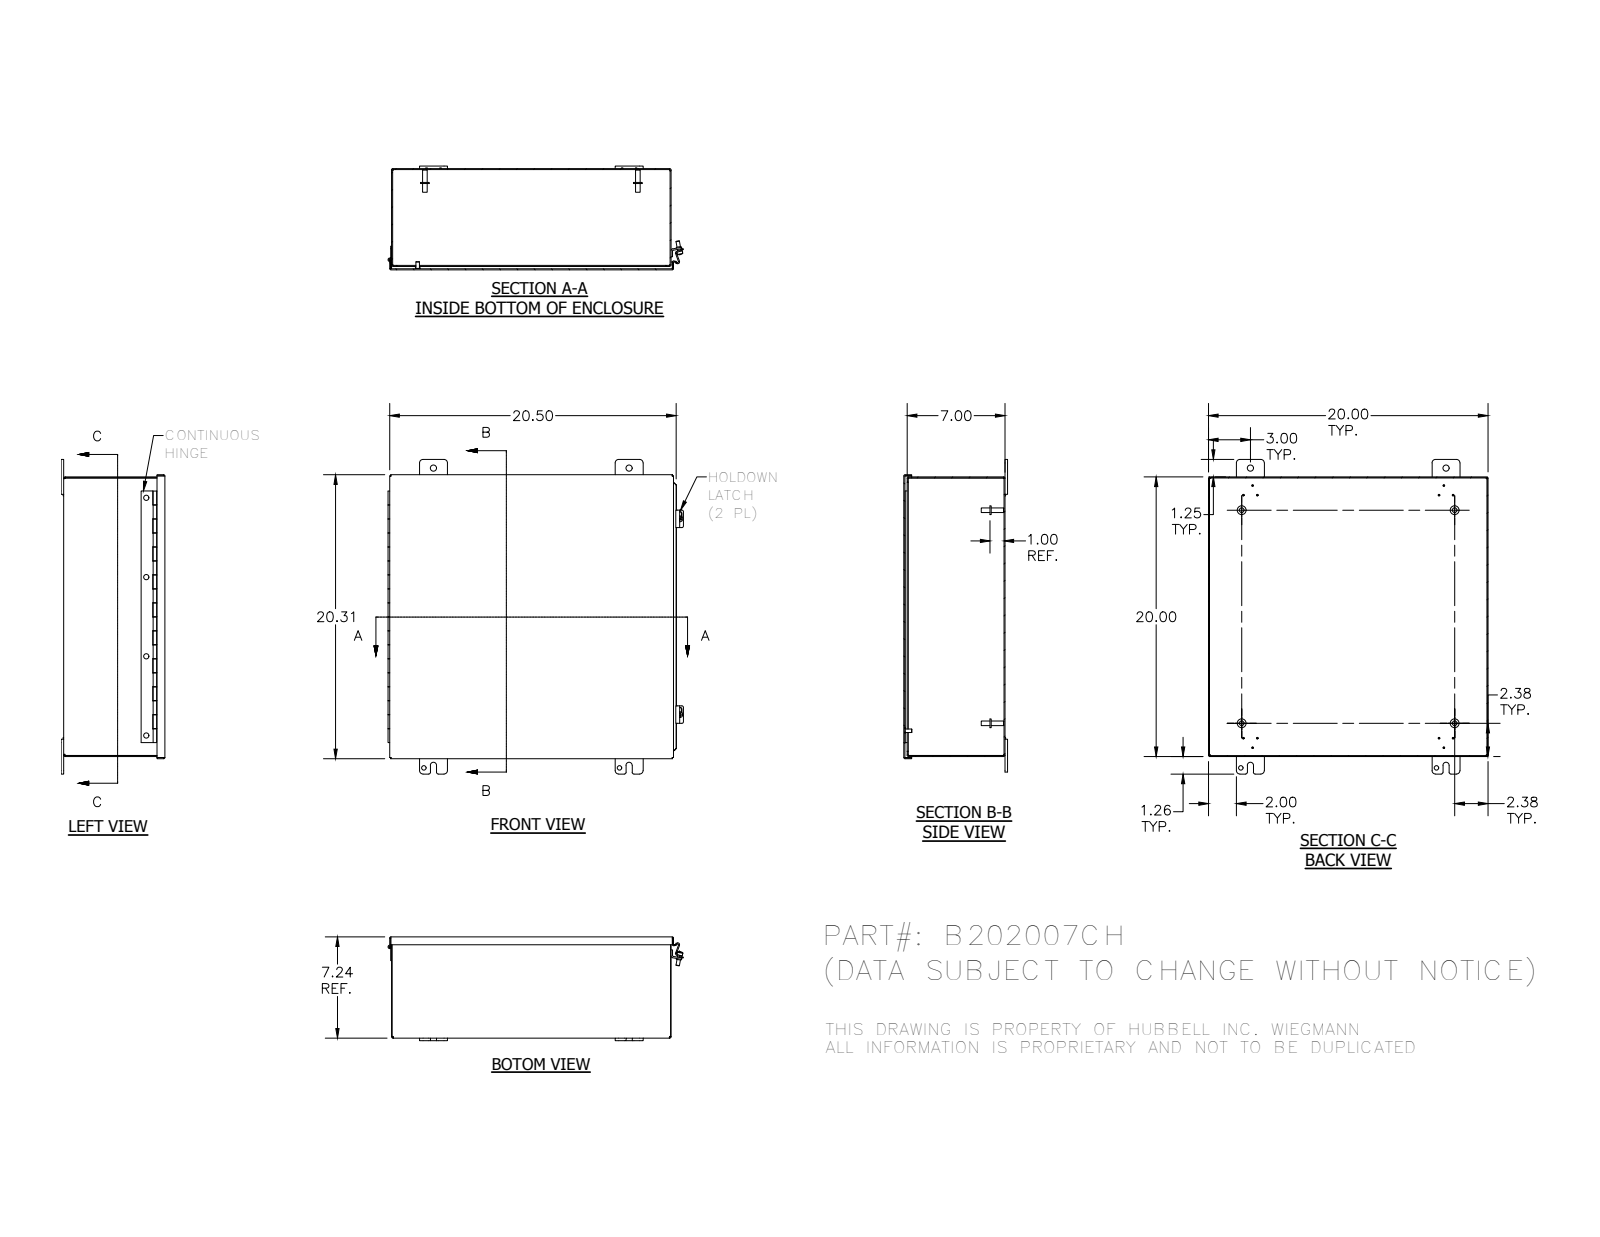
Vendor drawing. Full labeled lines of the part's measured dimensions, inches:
Part name (STEP PRODUCT): B202007CH; B202007CHBKP; B2020CHLID; H6010100 (+8 more)
STEP written by: Autodesk Inventor 2012 (AUTOMOTIVE_DESIGN)
Units: inches
Bodies: 20 solids, 617 faces (371 planar, 177 cylindrical, 69 other)
Overall size (bounding box): 22.505 × 21.136 × 7.423
Volume: 112.2 in³ · Surface area: 3 018 in²
Round holes (diameter × count): ⌀0.11 ×4, ⌀0.313 ×4, ⌀0.375 ×4, ⌀0.438 ×4, ⌀0.196 ×2, ⌀0.125 ×1, ⌀0.125 ×1
Round bosses / shafts (diameter × count): ⌀0.625 ×4, ⌀0.33 ×4, ⌀0.25 ×4, ⌀0.41 ×2, ⌀0.344 ×2, ⌀0.337 ×1, ⌀0.12 ×1
Partial cylindrical surfaces — rounded edges, fillets, slot ends (radius × count): R0.125 ×16, R0.25 ×16, R0.031 ×8, R0.063 ×8, R0.07 ×8, R0.105 ×8, R0.016 ×5, R0.09 ×5
Main face-to-face distances: 0.074, 7.169, 19.926, 7.243, 7.095, 20, 19.852, 20.063, 0.137, 6.926
Hole centre spacings: 14, 1.593, 20.005, 24.417, 0.75, 5.667, 13.39, 14
